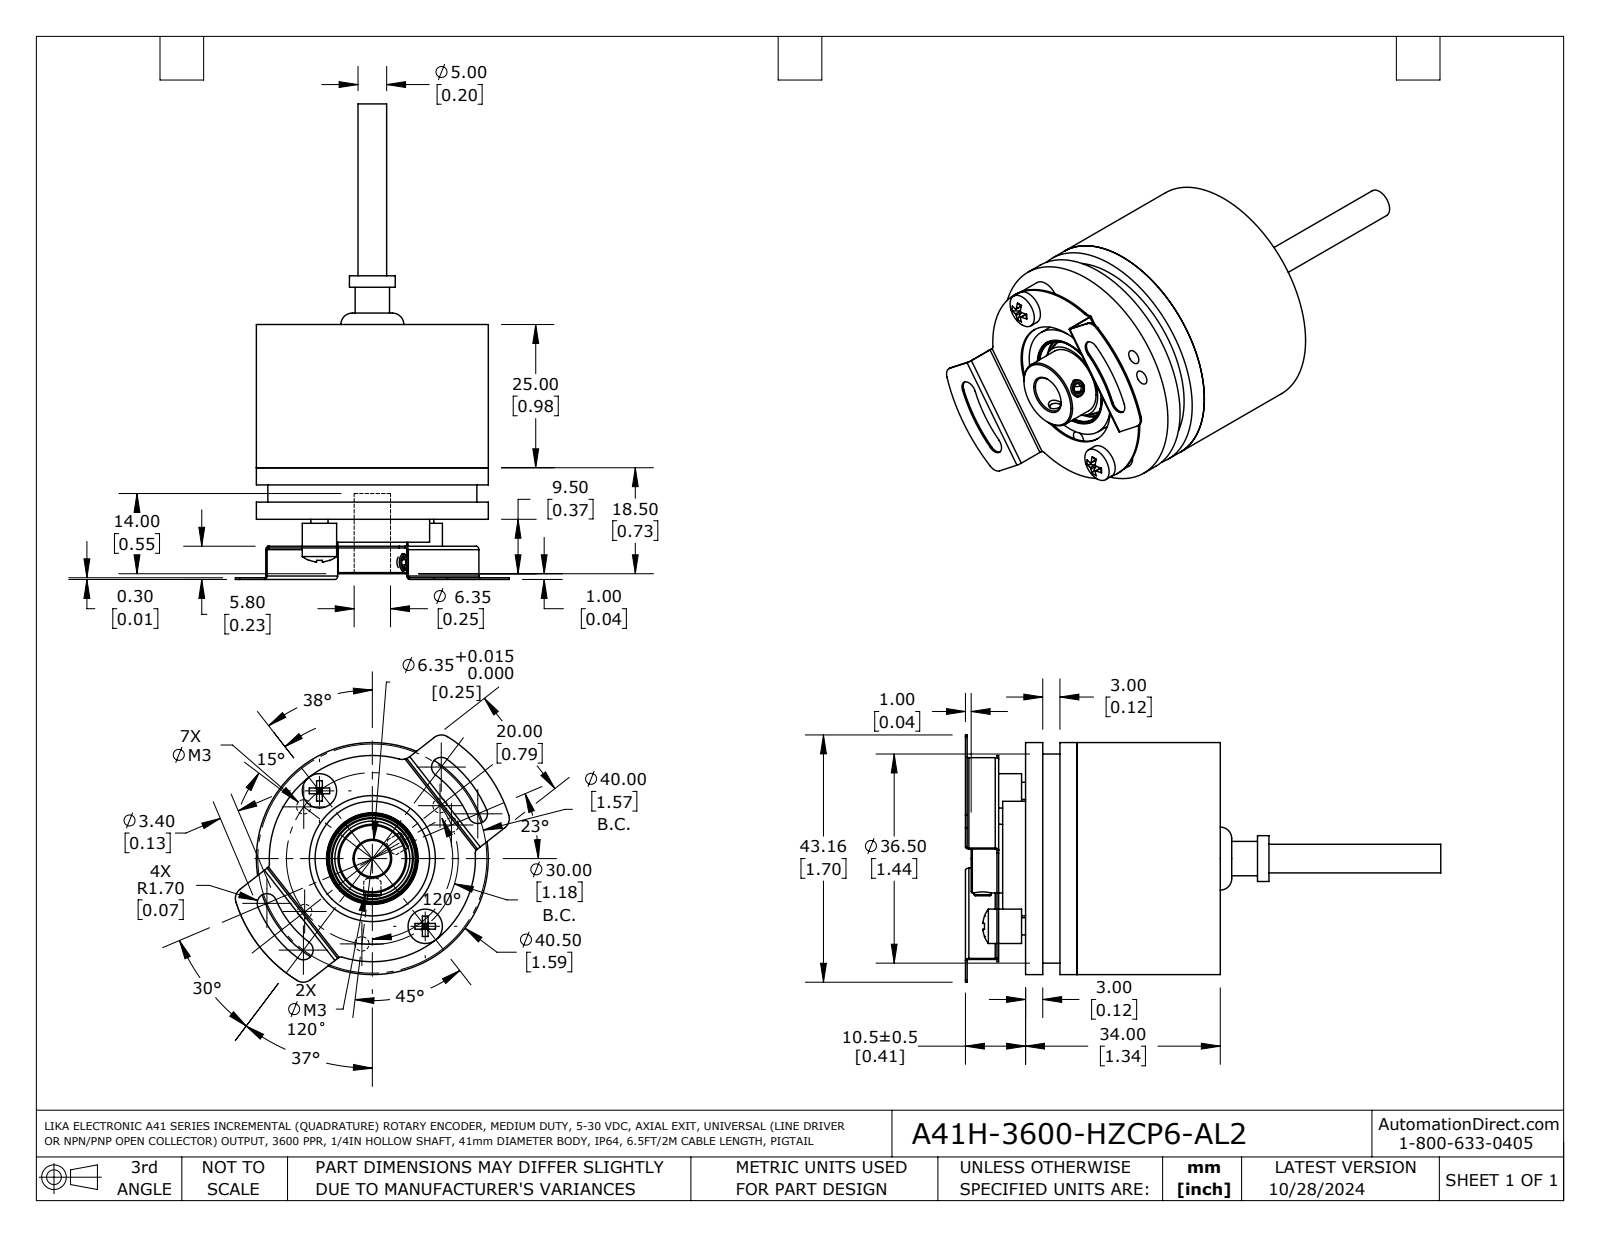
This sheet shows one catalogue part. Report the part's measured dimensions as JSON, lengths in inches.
{"part_name": "A41H-3600-HZCP6-AL2", "step_written_by": "SolidWorks 2021 (CONFIG_CONTROL_DESIGN)", "units": "inches", "bodies": {"solids": 15, "faces": 465, "planar": 139, "cylindrical": 186, "other": 140}, "overall_size": [3.268, 1.883, 1.699], "volume_in3": 1.187, "surface_area_in2": 32.38, "round_holes": [[0.098, 9], [0.063, 7], [0.157, 3], [0.087, 2], [0.126, 2], [0.138, 2], [0.169, 1], [0.25, 1], [0.295, 1], [0.512, 1], [0.602, 1], [0.612, 1]], "round_bosses_or_shafts": [[0.118, 4], [0.236, 3], [0.15, 2], [0.079, 2], [1.594, 1], [1.496, 1], [1.457, 1], [1.437, 1]], "partial_cylinders_radius": [[0.039, 14], [0.008, 8], [0.079, 5], [0.012, 4], [0.024, 4], [0.067, 4], [0.03, 3], [0.709, 1]], "face_to_face_distances": [0.118, 0.433, 1.339, 0.906, 0.197, 1.22, 0.079, 0.866, 0.039, 0.787], "hole_center_spacings": [0.591, 0.669, 0.835, 0.11, 0.118, 0.837, 0.945, 1.023]}
